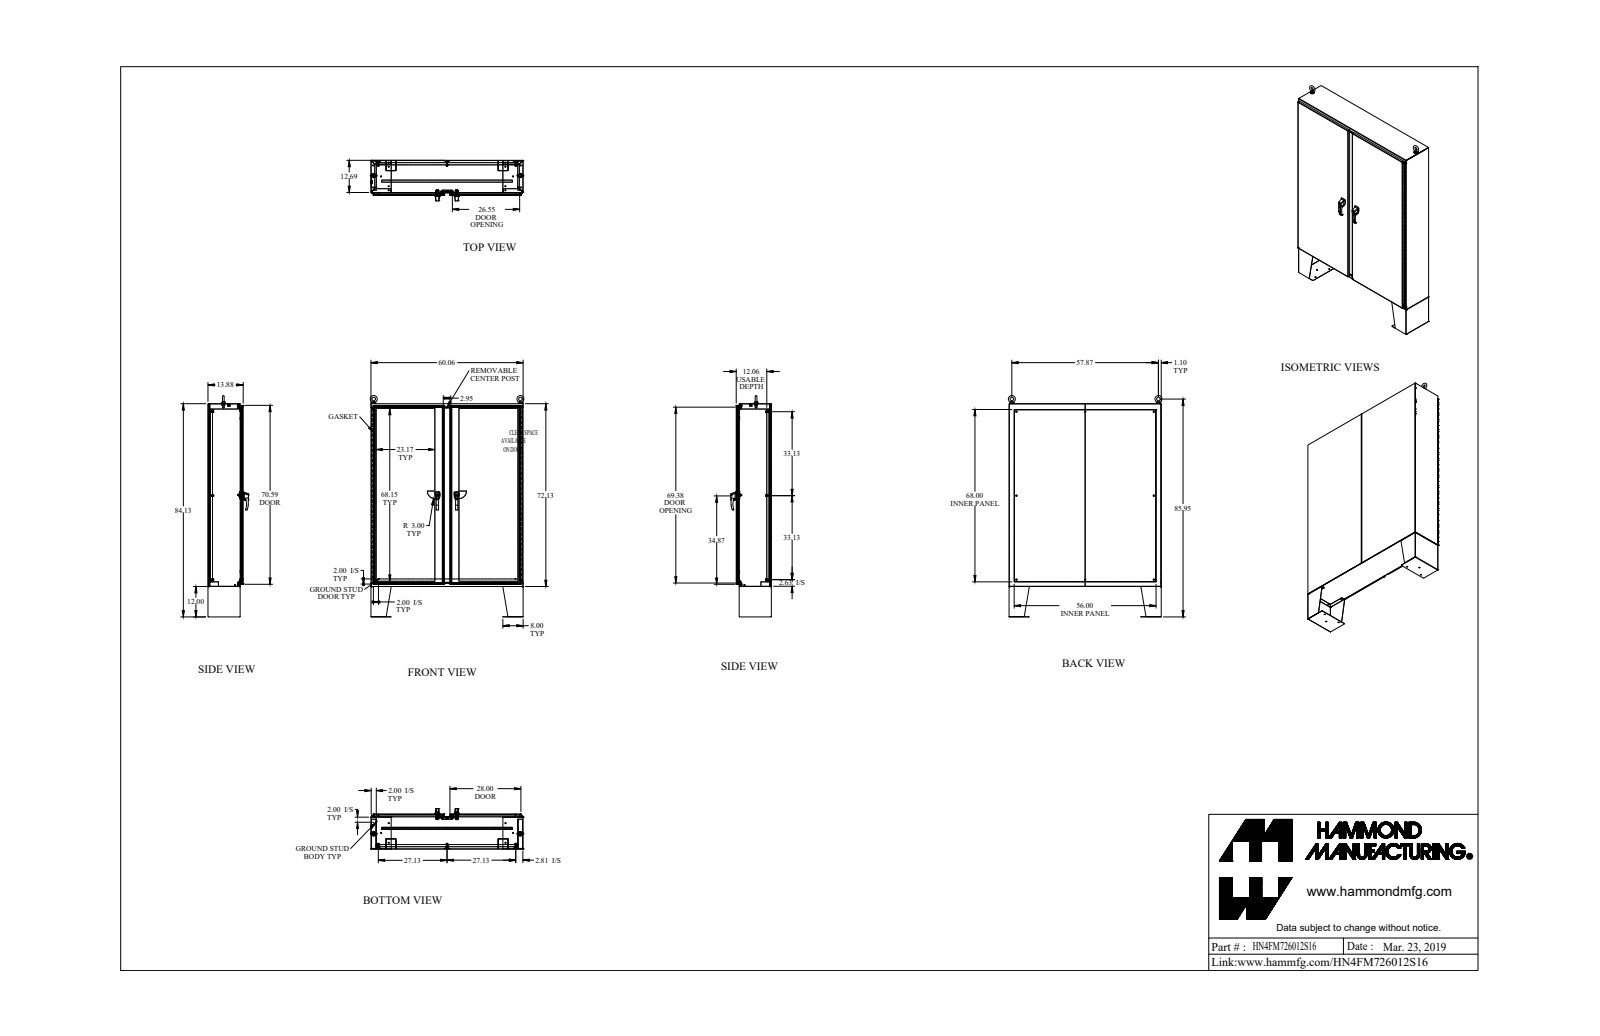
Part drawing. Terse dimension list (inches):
name: HN4FM726012S16
written by: SolidWorks 2018 (AUTOMOTIVE_DESIGN)
unit: in
bodies: 137 solids, 4026 faces (1850 planar, 1815 cylindrical, 361 other)
size: 87.321 × 60.607 × 15.99
volume: 2 024 in³; area: 40 752 in²
holes: 24× ⌀0.304, 14× ⌀0.437, 8× ⌀0.307, 8× ⌀0.35, 8× ⌀0.563, 6× ⌀0.25, 6× ⌀0.445, 4× ⌀0.281, 4× ⌀0.313, 4× ⌀0.39, 3× ⌀0.201, 3× ⌀0.313
bosses: 10× ⌀1, 8× ⌀0.65, 8× ⌀0.375, 8× ⌀0.332, 4× ⌀0.75, 4× ⌀0.625, 4× ⌀0.44, 4× ⌀0.37
rounds: 33× R0.5, 32× R0.018, 32× R0.125, 29× R0.048, 29× R0.143, 28× R0.06, 12× R0.03, 12× R0.09
face distances: 0.095, 13.78, 13.685, 0.125, 13.875, 11.998, 1.782, 1.687, 12.093, 1.657
hole spacings: 6, 12, 18, 24, 30, 36, 42, 1.61
